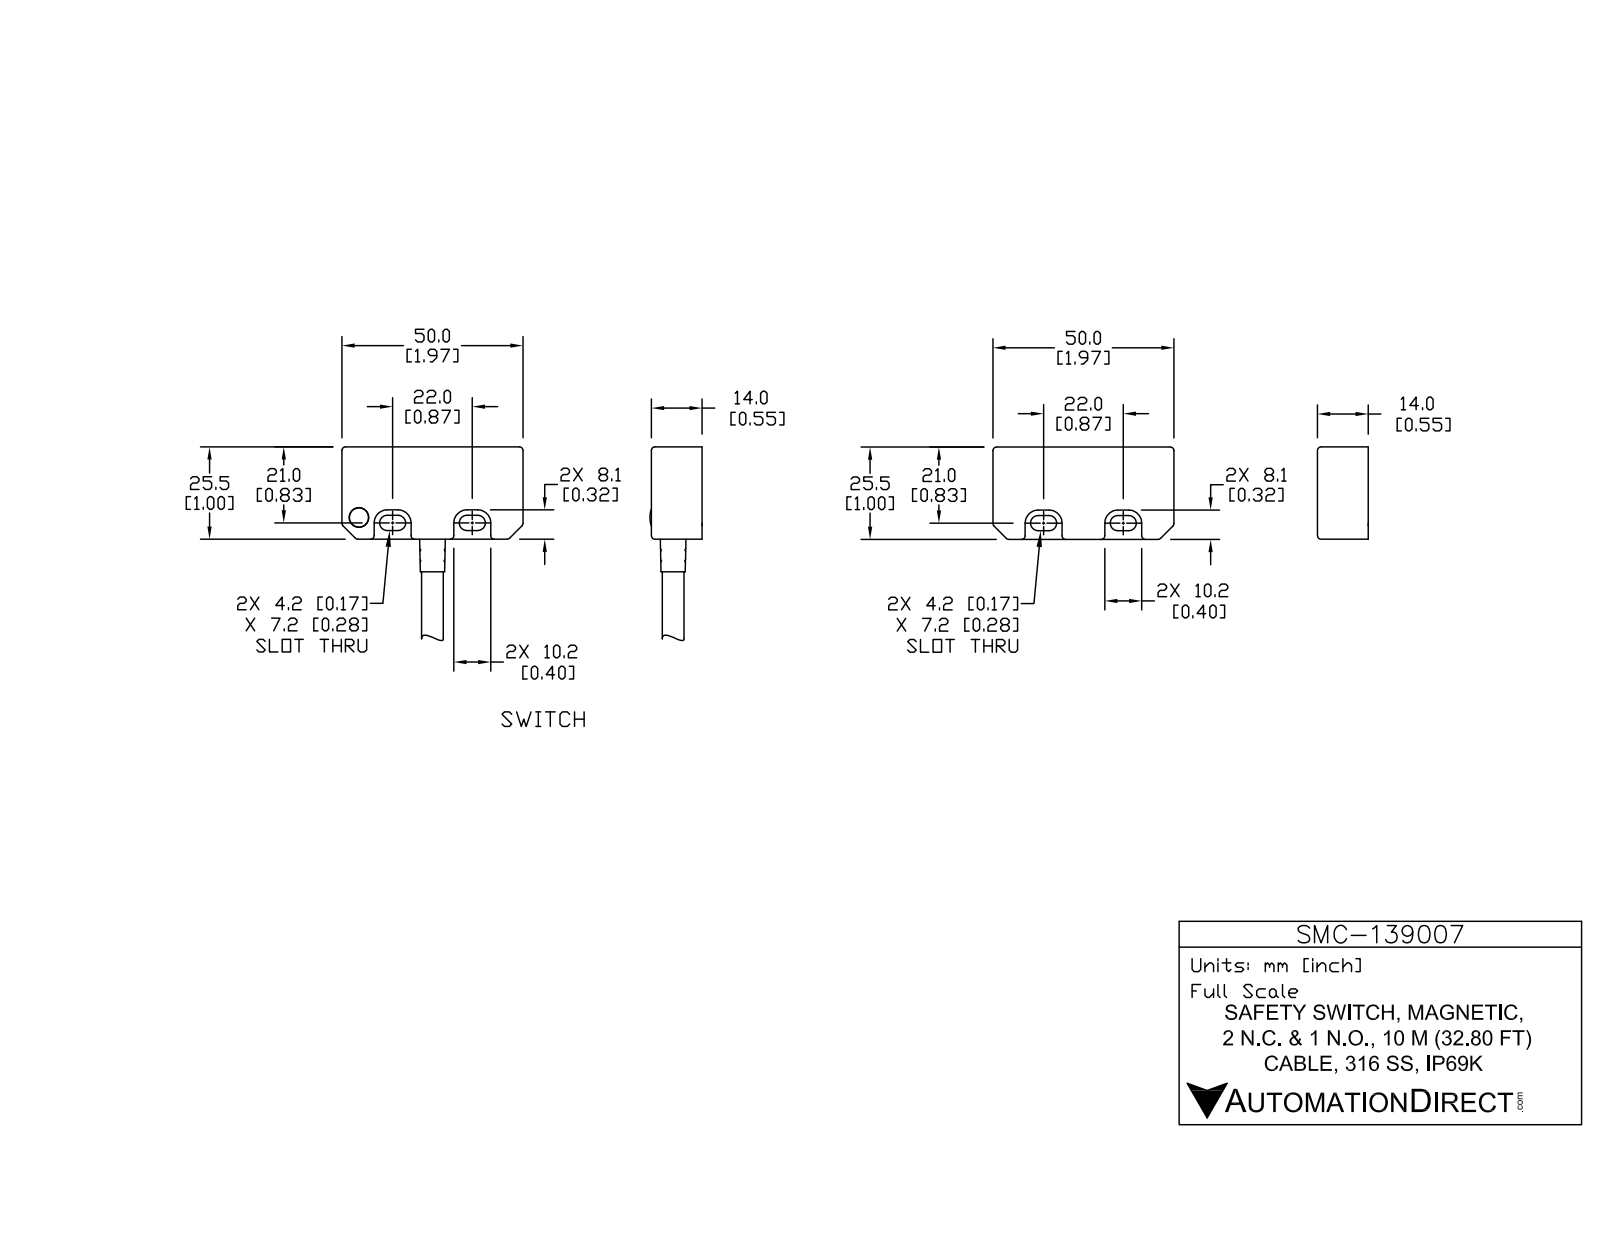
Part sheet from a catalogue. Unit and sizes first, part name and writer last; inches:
Units: inches
Overall size (bounding box): 8.091 × 1.969 × 0.566
Round holes (diameter × count): ⌀0.197 ×4, ⌀0.119 ×1, ⌀0.177 ×1, ⌀0.213 ×1, ⌀0.232 ×1, ⌀0.287 ×1
Round bosses / shafts (diameter × count): ⌀0.193 ×4, ⌀0.079 ×4, ⌀0.031 ×2, ⌀0.339 ×1, ⌀0.299 ×1, ⌀0.28 ×1, ⌀0.236 ×1, ⌀0.209 ×1
Partial cylindrical surfaces — rounded edges, fillets, slot ends (radius × count): R0.02 ×80, R0.012 ×74, R0.039 ×40, R0.083 ×8, R0.122 ×8, R0.128 ×8, R0.142 ×8, R0.175 ×8
Main face-to-face distances: 0.059, 0.543, 0.055, 0.488, 0.484, 0.429, 0.098, 0.945, 1.043, 1.909
Hole centre spacings: 0.866, 0.988, 0.472, 1.27, 1.309, 1.319, 1.332, 1.775
Volume: 1.16 in³ · Surface area: 36.28 in²
Bodies: 12 solids, 886 faces (254 planar, 373 cylindrical, 259 other)
Part name (STEP PRODUCT): SMC-139007_2; SMC-139007_1; SMC-139007
STEP written by: SolidWorks 2017 (AUTOMOTIVE_DESIGN)
